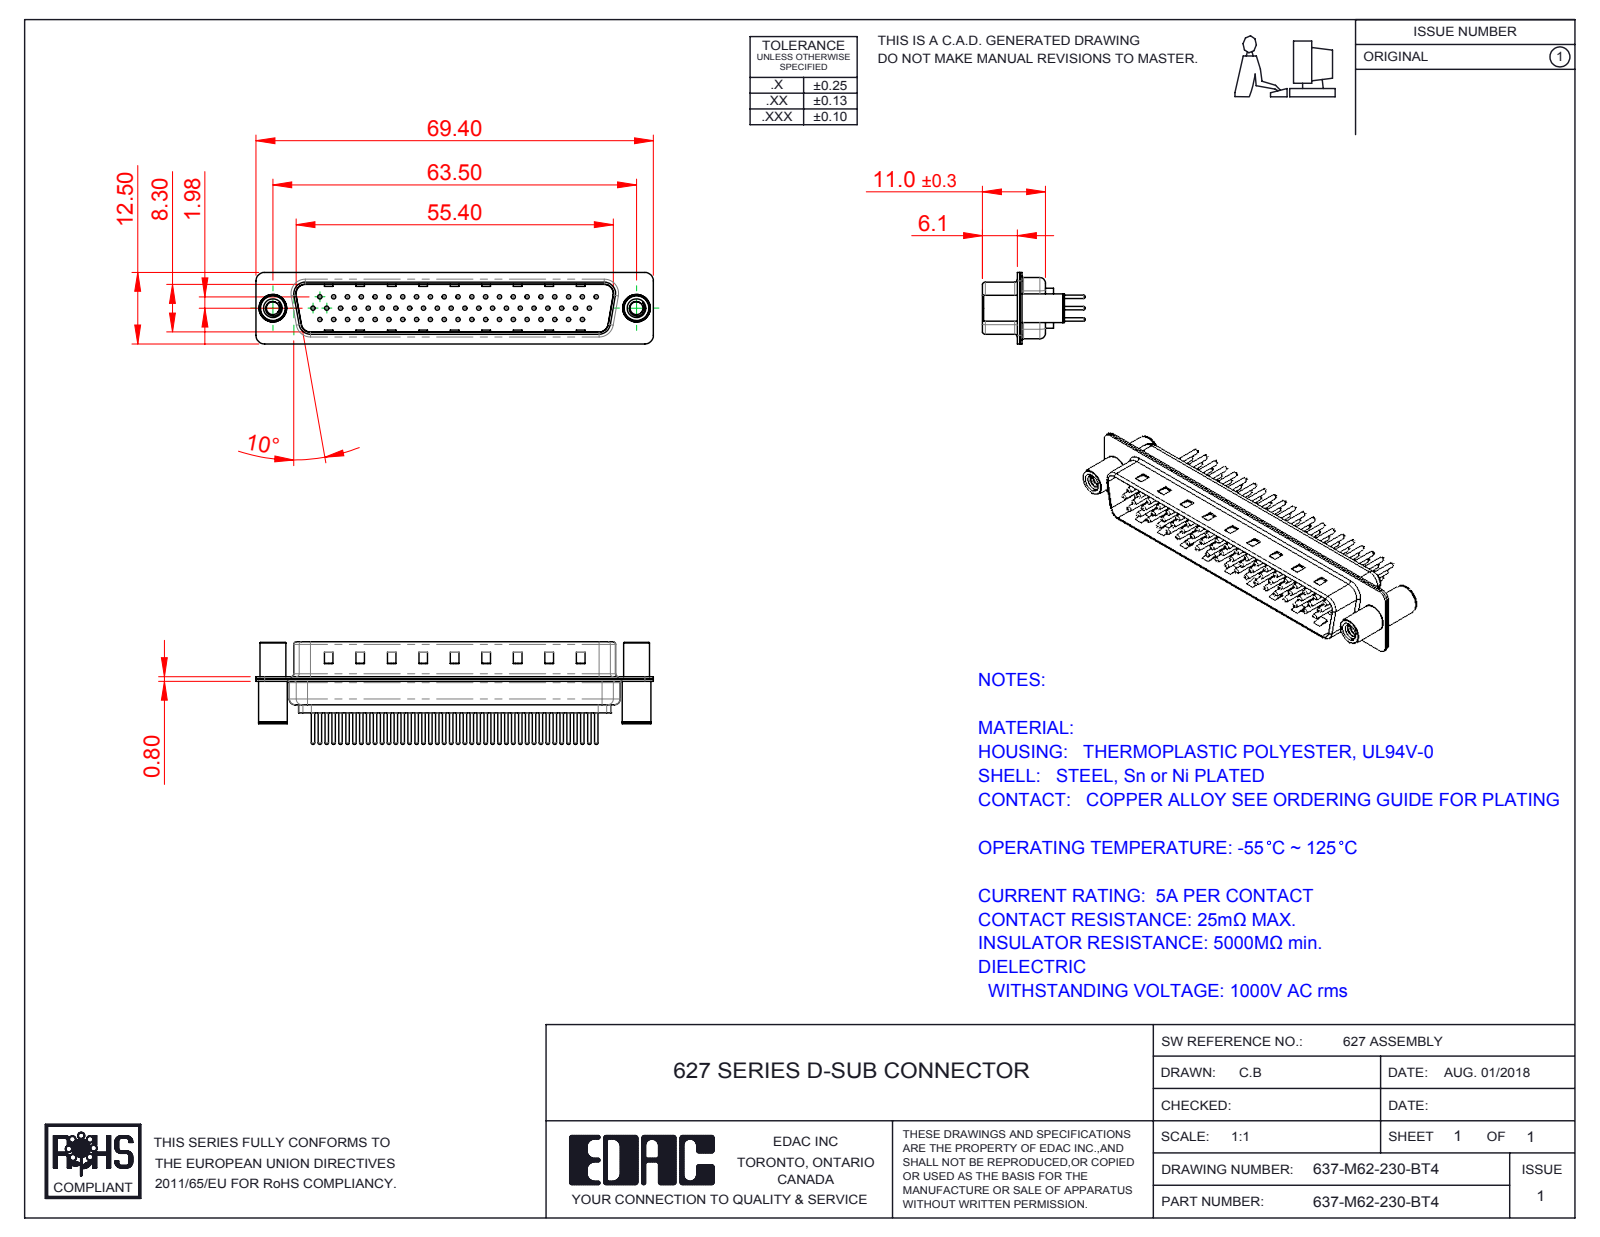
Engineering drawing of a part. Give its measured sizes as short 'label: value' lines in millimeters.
name: 637M Housing_62 Contacts; 637M Contact Row 2_30; 637M Shell Front_62 Contacts; 637M Shell Rear_62 Contacts (+4 more)
written by: SolidWorks 2016 (CONFIG_CONTROL_DESIGN)
unit: mm
bodies: 67 solids, 2792 faces (643 planar, 1061 cylindrical, 1088 other)
size: 69.4 × 17.9 × 12.5
volume: 4 205 mm³; area: 11 942 mm²
holes: 62× ⌀0.75, 62× ⌀1.6, 62× ⌀2, 2× ⌀2.26, 2× ⌀3.26, 2× ⌀4, 2× ⌀4.8
bosses: 62× ⌀1.5, 62× ⌀0.6, 2× ⌀5, 2× ⌀4.9, 2× ⌀4.5
rounds: 16× R1.5, 12× R2, 8× R0.5, 8× R1.6, 4× R0.25, 4× R0.6, 4× R0.65, 4× R0.9
face distances: 0.4, 0.8, 9.5, 9.1, 8.7, 9.9, 0.75, 0.35, 5.9, 1.2
hole spacings: 7.24, 2.32, 2.41, 4.13, 9.65, 4.83, 14.48, 11.04
